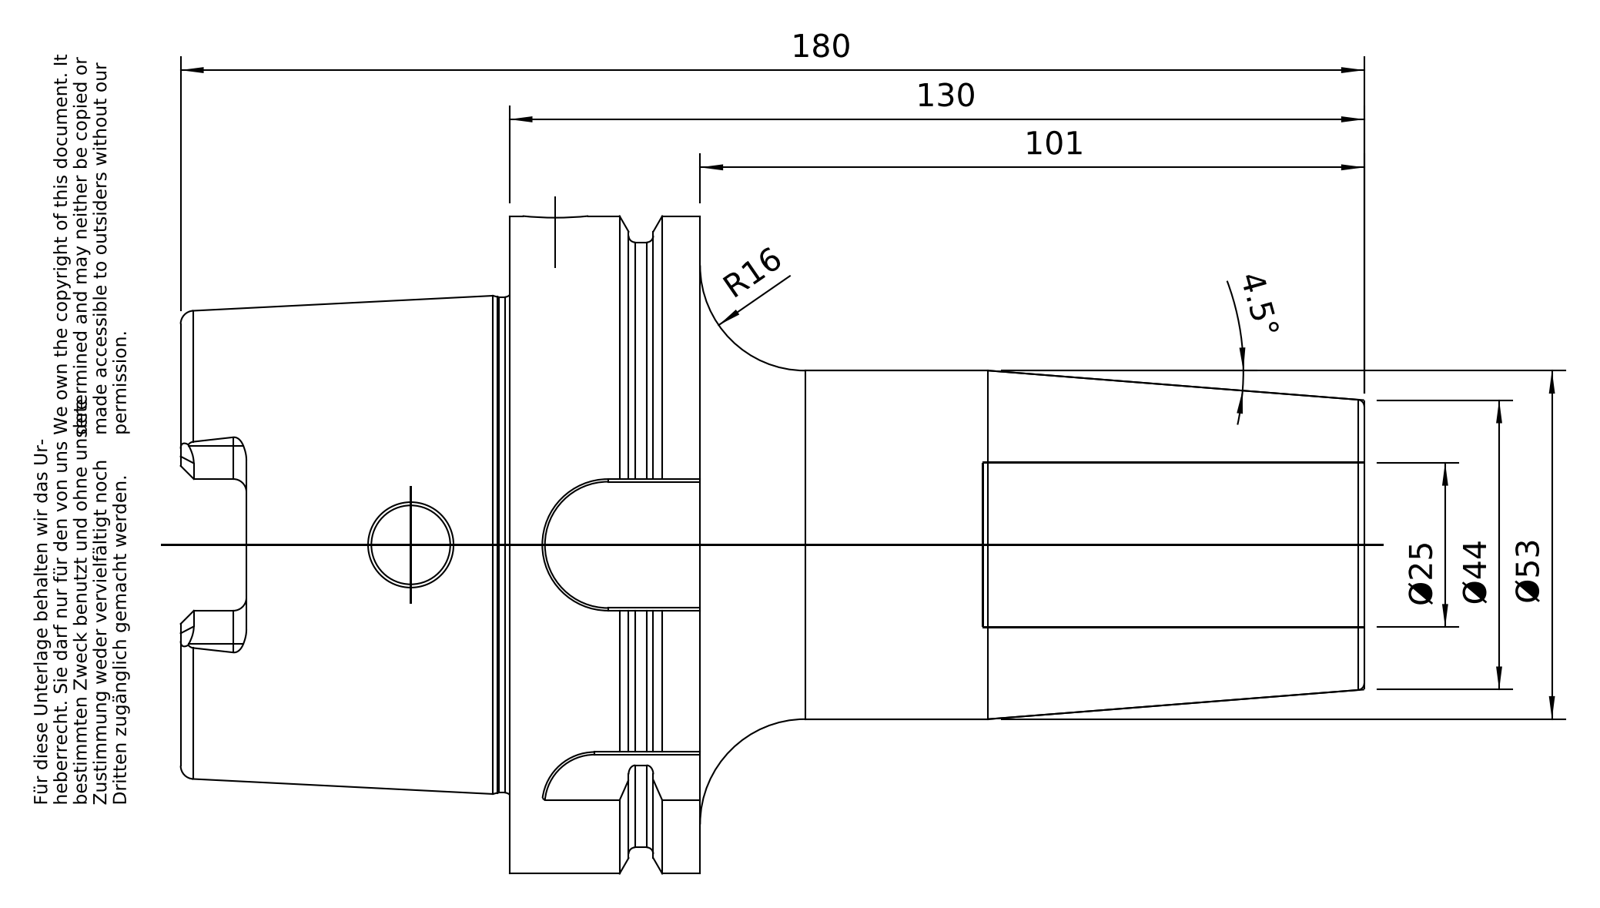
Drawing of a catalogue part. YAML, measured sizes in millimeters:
part_name: "A100-144-25"
step_written_by: "PRO/ENGINEER BY PARAMETRIC TECHNOLOGY CORPORATION, 2010430 (CONFIG_CONTROL_DESIGN)"
units: millimeters
bodies: {solids: 1, faces: 174, planar: 50, cylindrical: 51, other: 73}
overall_size: [180, 100, 100]
volume: 438712
surface_area: 69062
round_holes:
  - {diameter: 10, count: 1}
  - {diameter: 12, count: 1}
  - {diameter: 22.5, count: 1}
  - {diameter: 24, count: 1}
  - {diameter: 24.32, count: 1}
  - {diameter: 24.5, count: 1}
  - {diameter: 25, count: 1}
  - {diameter: 53, count: 1}
  - {diameter: 63, count: 1}
round_bosses_or_shafts:
  - {diameter: 100, count: 1}
  - {diameter: 92, count: 1}
  - {diameter: 75.36, count: 1}
partial_cylinders:
  - {radius: 2, count: 6}
  - {radius: 5, count: 4}
  - {radius: 8, count: 1}
  - {radius: 10, count: 1}
  - {radius: 11, count: 1}
face_to_face_distances: [29, 12.5, 16.5, 130, 117.5, 101, 50, 62.5, 79, 180]
